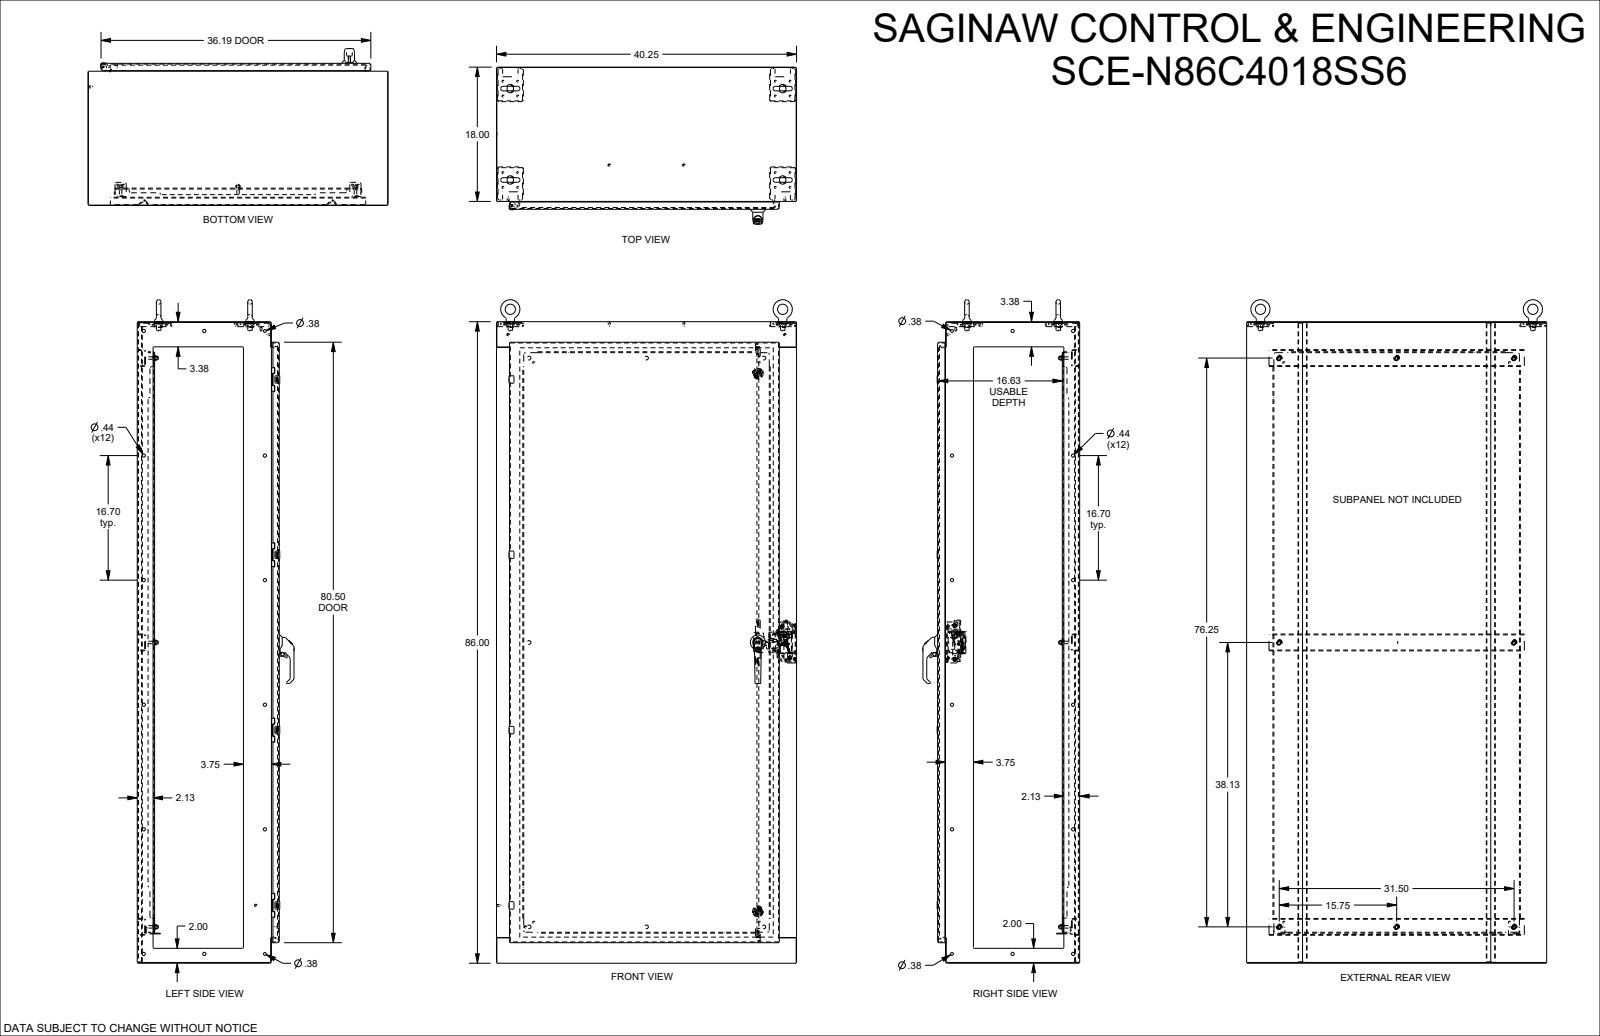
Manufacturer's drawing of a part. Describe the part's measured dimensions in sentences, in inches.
The part is named "SCE-N86C4018". Its 3-D file was written by "SolidWorks 2023 (AUTOMOTIVE_DESIGN)". It is 30 solids with 4231 faces: 1657 planar, 1492 cylindrical and 1082 other. Overall it measures 88.945 by 40.25 by 21.046 inches. Its volume is 1 155 cubic inches and its surface area 21 793 square inches. Round holes: 18 of diameter 0.25, 12 of diameter 0.437, 10 of diameter 0.375, 8 of diameter 0.205, 8 of diameter 0.244, 4 of diameter 0.04, 4 of diameter 0.17, 4 of diameter 0.218, 4 of diameter 0.256, 4 of diameter 0.875, 2 of diameter 0.135, 2 of diameter 0.156. Round bosses or shafts: 12 of diameter 0.17, 11 of diameter 0.25, 8 of diameter 0.24, 5 of diameter 0.196, 4 of diameter 1.173, 4 of diameter 0.6, 2 of diameter 1.4, 2 of diameter 0.48. Partial cylindrical surfaces (rounded edges, fillets, slot ends): 129 of radius 0.03, 108 of radius 0.015, 87 of radius 0.125, 42 of radius 0.063, 38 of radius 0.167, 37 of radius 0.02, 32 of radius 0.229, 27 of radius 0.25. The main face-to-face distances are 0.104, 18.954, 19.058, 18.85, 17.896, 1.058, 85.896, 0.104, 40.146, 17.792. The hole center spacings are 1.979, 1.4, 23.5, 16.7, 23.302, 2.799, 11.304, 12.25.
